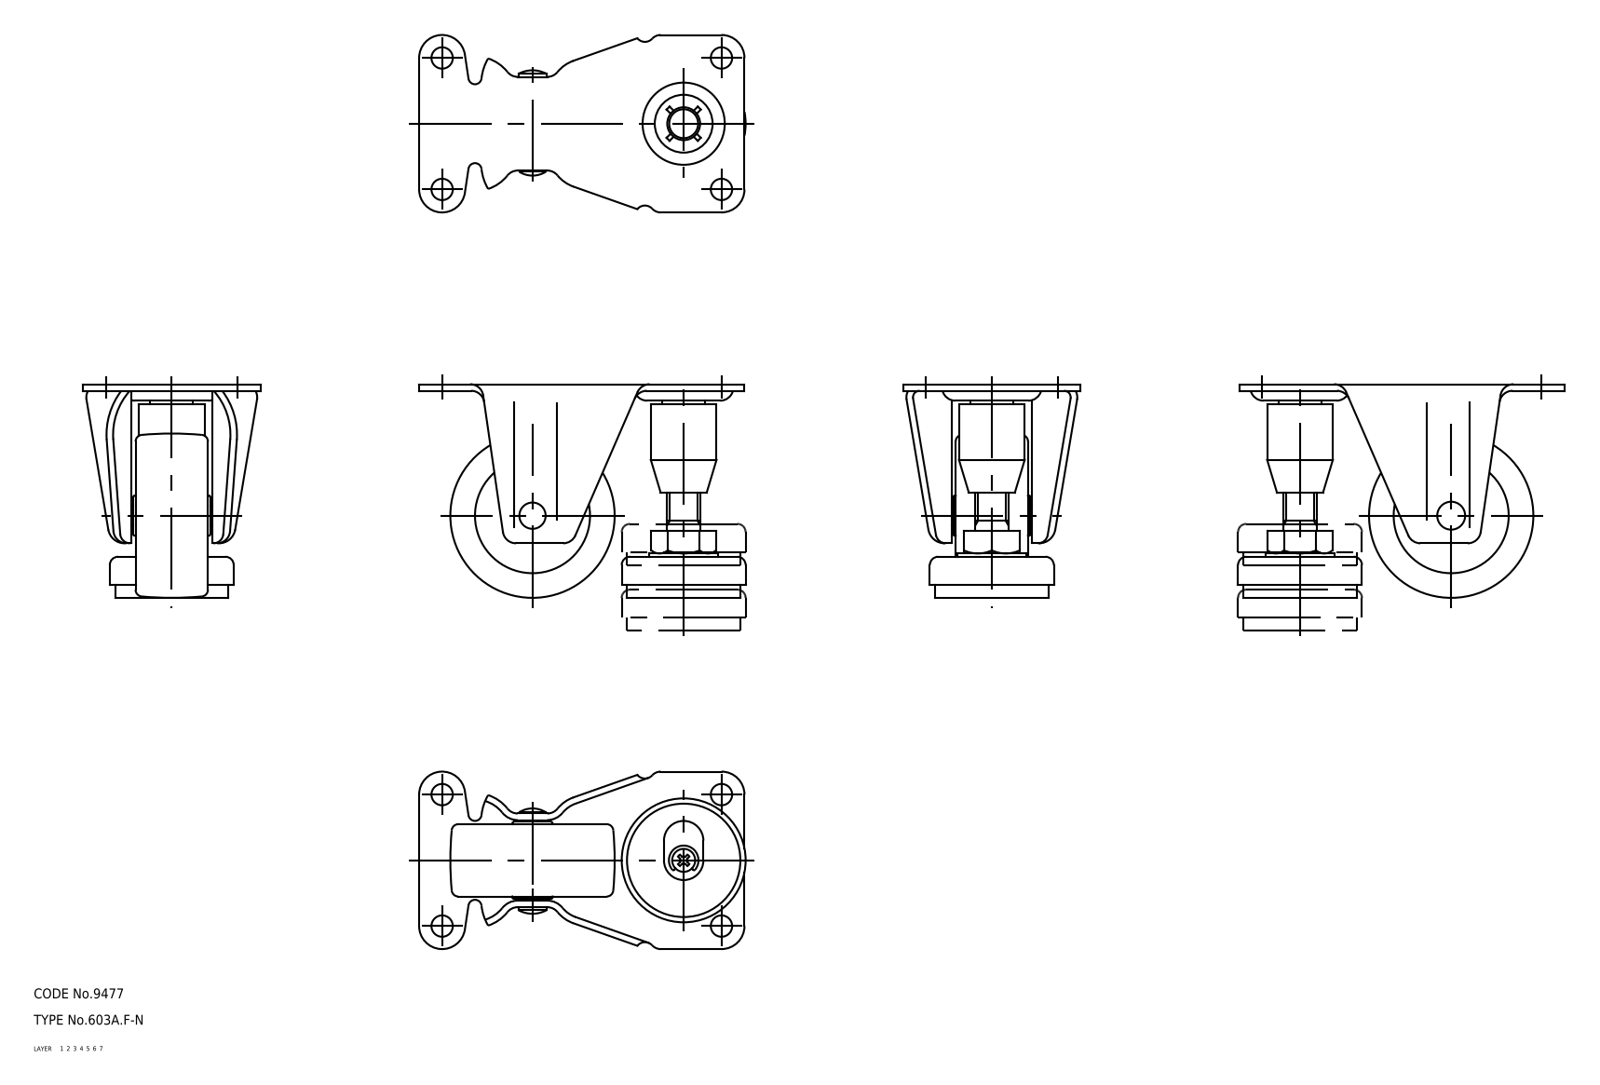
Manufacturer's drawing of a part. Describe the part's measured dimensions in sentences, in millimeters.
The part is named "wheel; foot; axle; No_603A_F_N_14153_36". Its 3-D file was written by "CADfix (AUTOMOTIVE_DESIGN)". It is 7 solids with 253 faces: 0 planar, 0 cylindrical and 253 other. Overall it measures 99.35 by 65 by 54 millimeters. Its volume is 71 095 cubic millimeters and its surface area 33 818 square millimeters.
